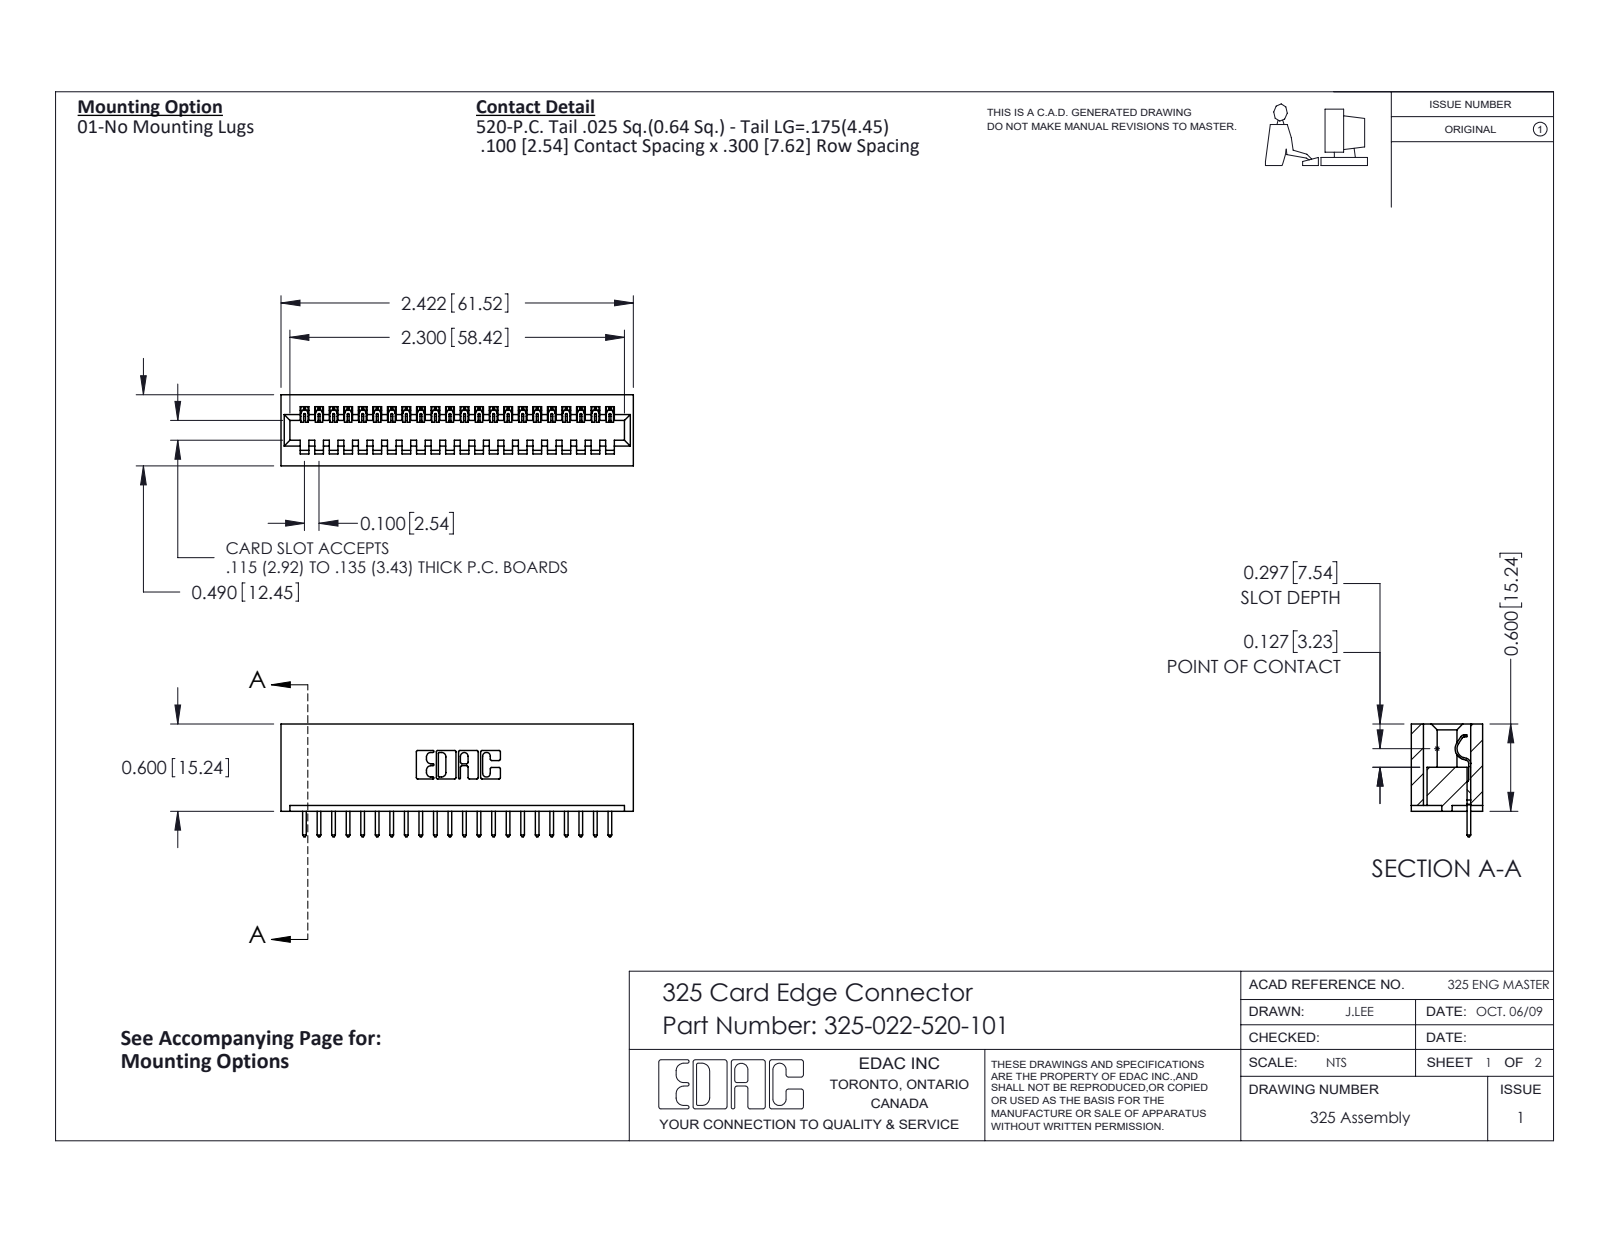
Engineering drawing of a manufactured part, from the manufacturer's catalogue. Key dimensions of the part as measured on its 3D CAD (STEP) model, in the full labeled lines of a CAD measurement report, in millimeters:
Part name (STEP PRODUCT): 325 Part_Lugless; 325-022-520-101; 325-292-001_325-293-120
STEP written by: SolidWorks 2016 (CONFIG_CONTROL_DESIGN)
Units: millimetres
Bodies: 23 solids, 1382 faces (990 planar, 392 cylindrical, 0 other)
Overall size (bounding box): 61.5 × 19.7 × 12.4
Volume: 8 160 mm³ · Surface area: 8 845 mm²
Partial cylindrical surfaces — rounded edges, fillets, slot ends (radius × count): R0.2 ×44, R0.3 ×44, R0.3 ×22, R0.2 ×6, R0.8 ×6, R0.7 ×3, R0.4 ×1, R0.6 ×1
Main face-to-face distances: 2.1, 10.3, 7.6, 12.4, 2.7, 9.7, 0.6, 2.5, 14.2, 8.3
